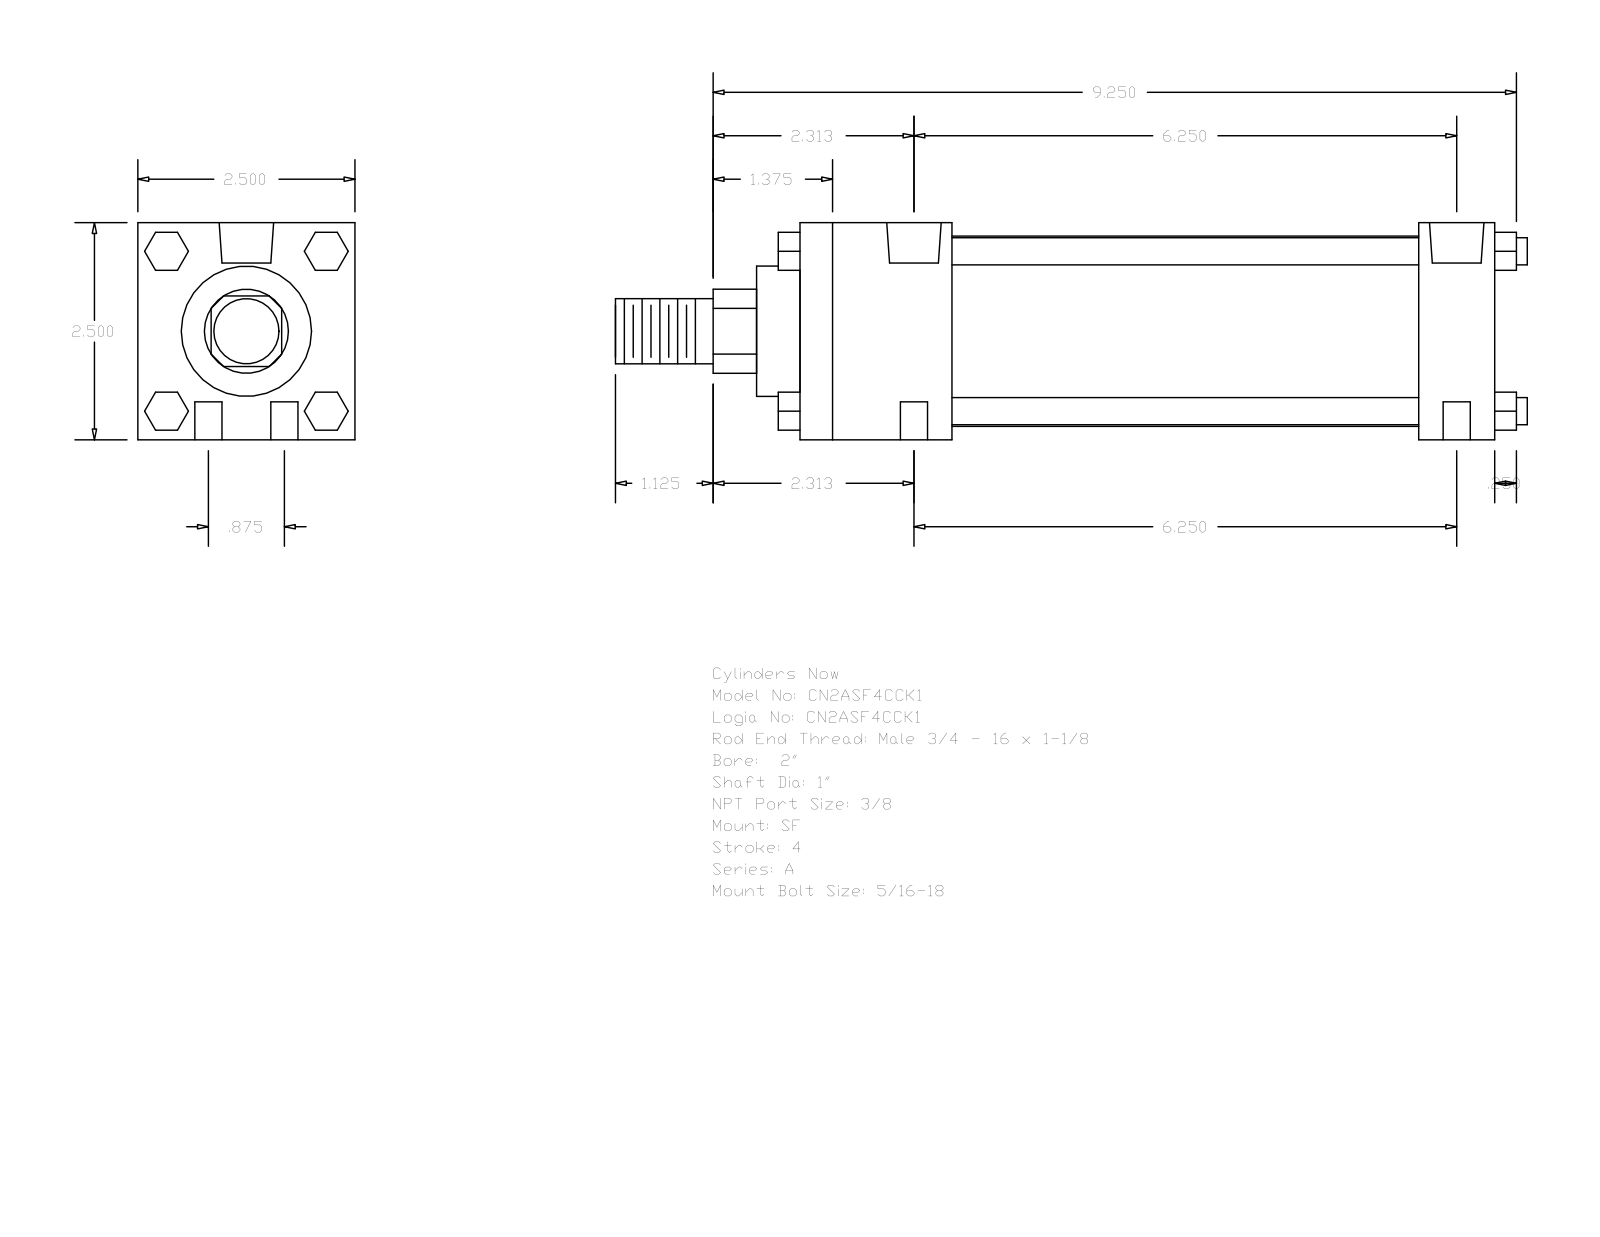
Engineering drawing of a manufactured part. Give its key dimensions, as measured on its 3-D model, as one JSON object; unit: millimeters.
{"part_name": "A_SF__0200_1", "step_written_by": "GSSL Pune (CONFIG_CONTROL_DESIGN)", "units": "millimeters", "bodies": {"solids": 0, "faces": 124, "planar": 94, "cylindrical": 30, "other": 0}, "overall_size": [266.7, 63.5, 63.5], "round_holes": [[7.94, 4], [5.56, 2], [15.93, 2]], "round_bosses_or_shafts": [[7.94, 4], [55.63, 1], [38.1, 1], [25.4, 1], [19.05, 1]], "partial_cylinders_radius": [[12.29, 1]], "face_to_face_distances": [63.5, 203.2, 180.98, 22.22, 44.45, 136.53, 158.75, 12.7, 215.9, 6.35], "hole_center_spacings": [11.11, 159.14, 158.75, 22.22, 160.3, 153.18]}
